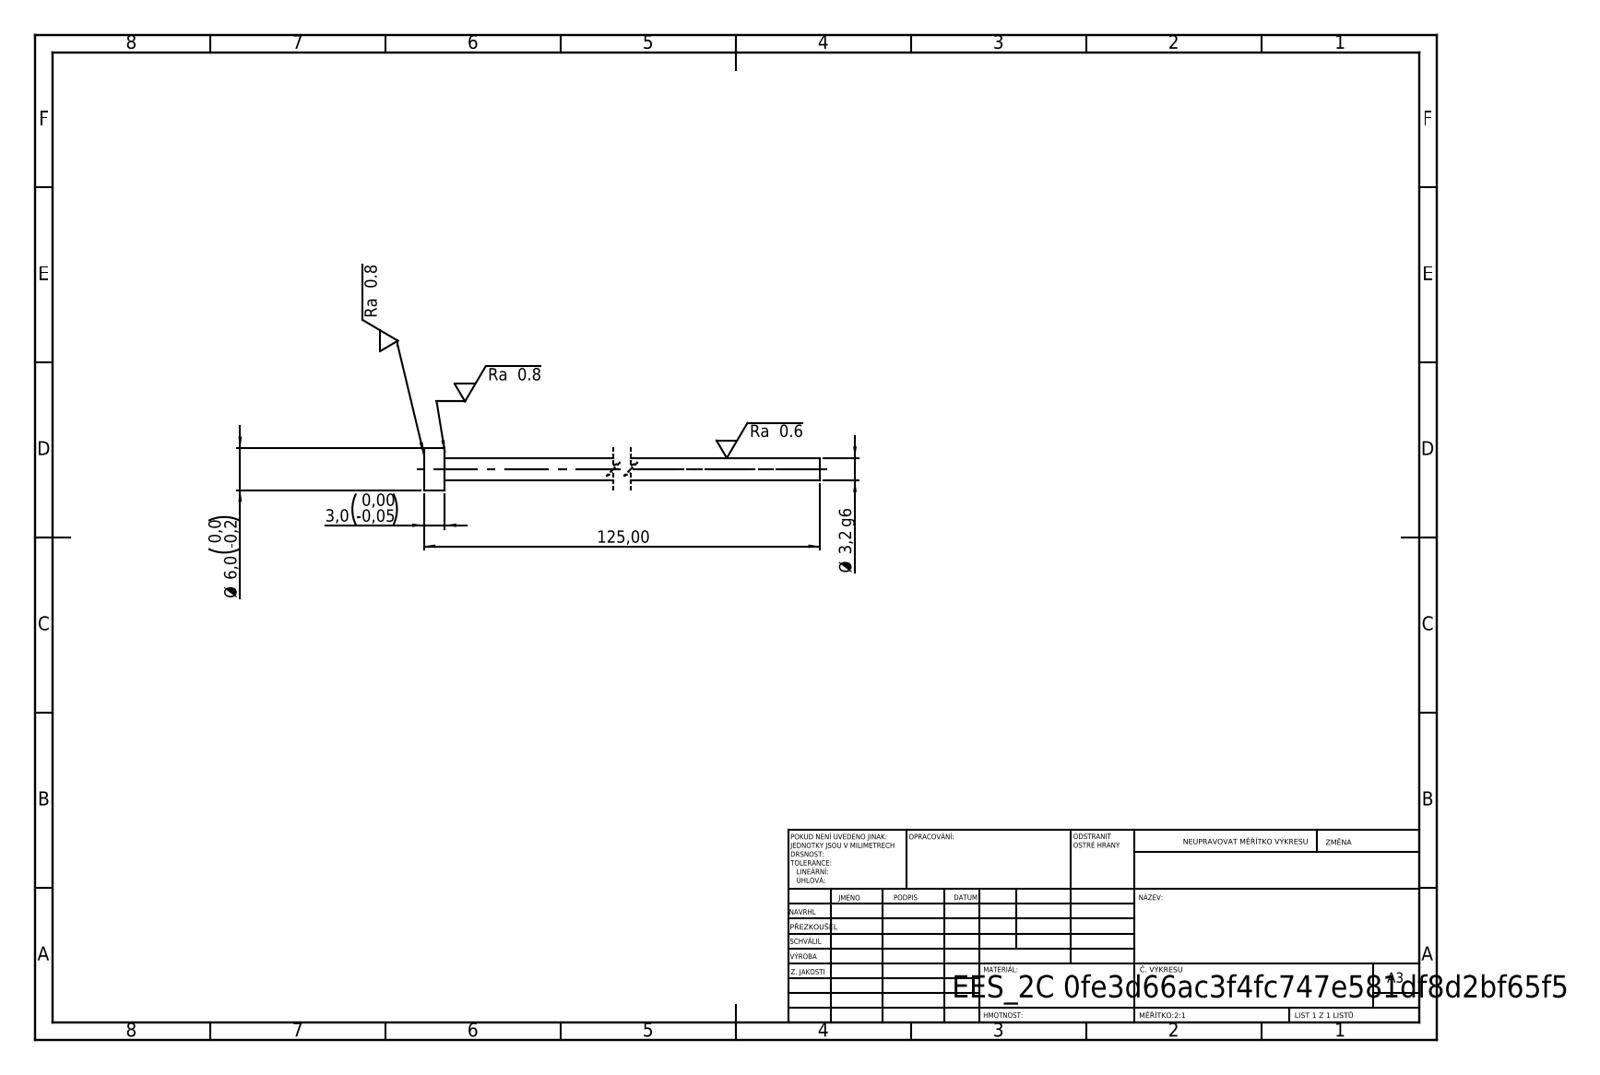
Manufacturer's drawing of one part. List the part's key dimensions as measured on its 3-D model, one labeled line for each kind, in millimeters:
STEP written by: SolidWorks 2019 (CONFIG_CONTROL_DESIGN)
Units: millimetres
Bodies: 1 solid, 7 faces (3 planar, 4 cylindrical, 0 other)
Overall size (bounding box): 125 × 6 × 6
Volume: 1 066 mm³ · Surface area: 1 340 mm²
Round bosses / shafts (diameter × count): ⌀6 ×1, ⌀3.2 ×1
Main face-to-face distances: 3, 125, 122
